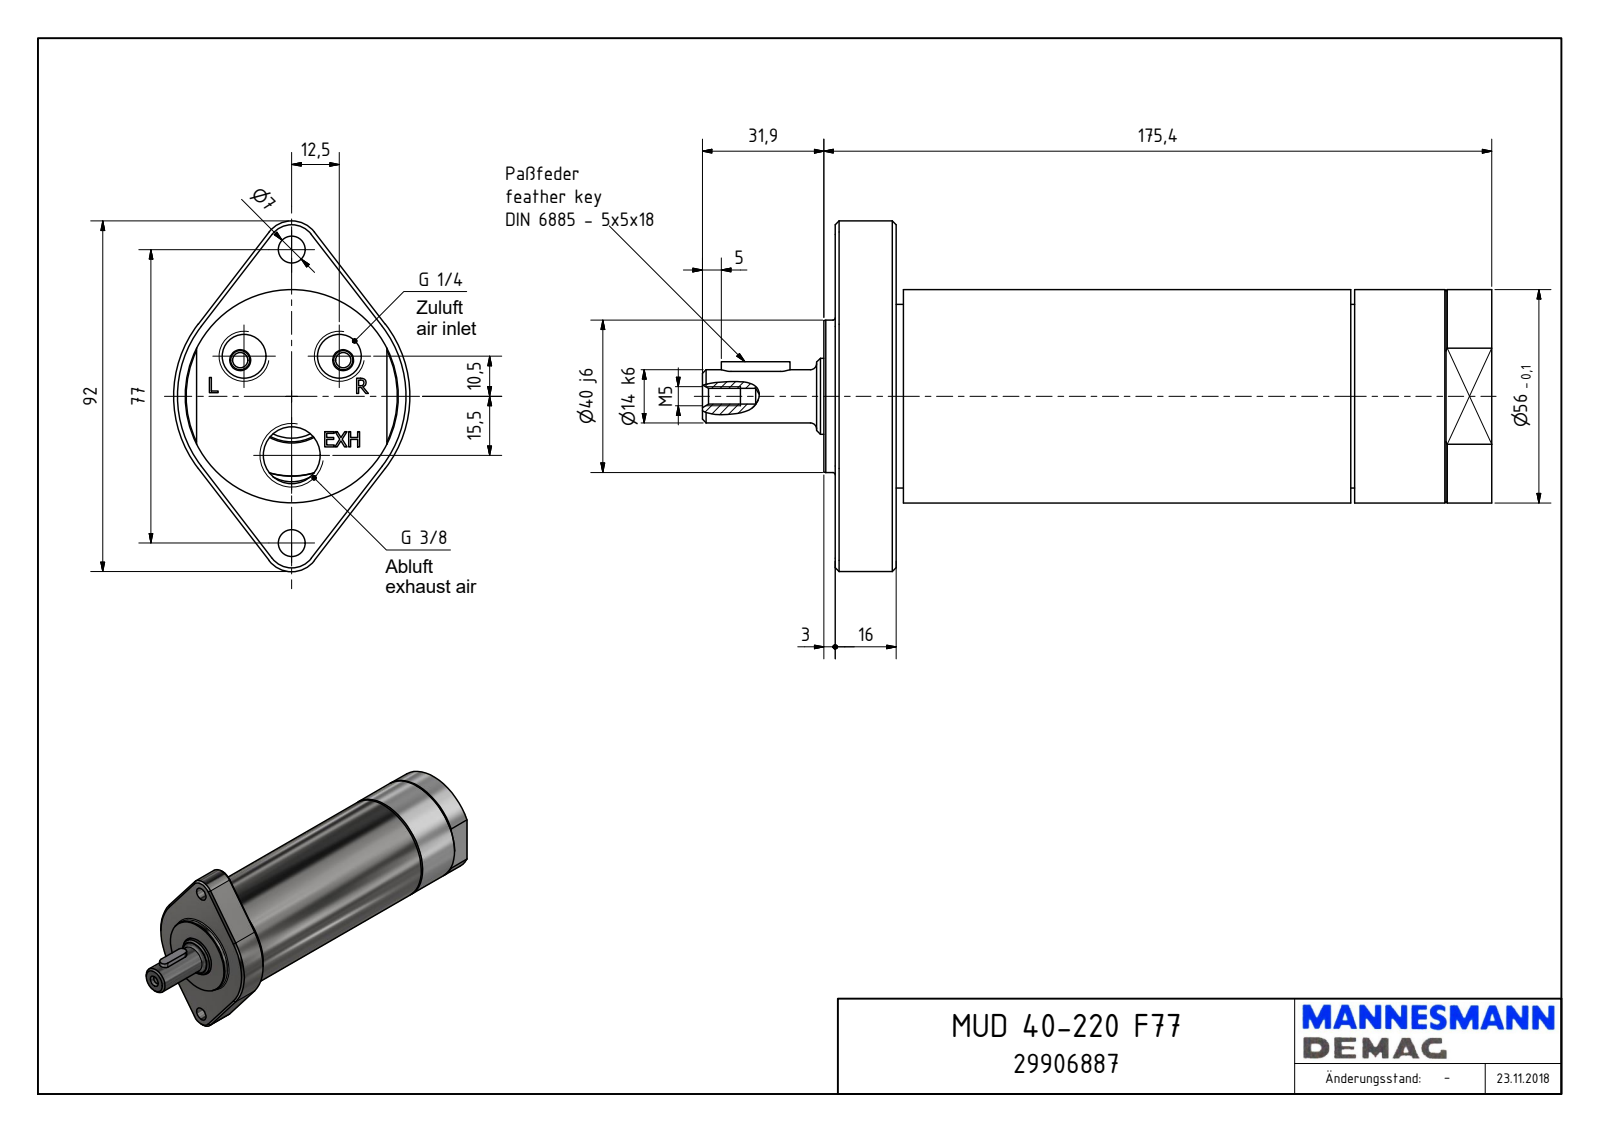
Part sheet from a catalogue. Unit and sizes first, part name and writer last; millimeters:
Units: millimetres
Overall size (bounding box): 207.3 × 92 × 62
Round holes (diameter × count): ⌀7 ×2, ⌀11.45 ×2, ⌀4.13 ×1, ⌀14.95 ×1, ⌀21 ×1, ⌀21.25 ×1, ⌀23.54 ×1, ⌀26 ×1, ⌀48.38 ×1
Round bosses / shafts (diameter × count): ⌀56 ×1, ⌀48.18 ×1, ⌀40 ×1, ⌀19.95 ×1, ⌀14 ×1
Partial cylindrical surfaces — rounded edges, fillets, slot ends (radius × count): R2.5 ×2, R6 ×2, R7.5 ×2, R19.57 ×1, R23 ×1, R31 ×1
Main face-to-face distances: 172.4, 16, 156.4, 3, 19, 175.4, 1.9, 20.9, 17.9, 154.5
Hole centre spacings: 16.32, 28.85, 30.66, 38.5, 50.57, 15.5, 23, 25
Volume: 444 470 mm³ · Surface area: 47 913 mm²
Bodies: 1 solid, 195 faces (105 planar, 36 cylindrical, 54 other)
Part name (STEP PRODUCT): MUD 40-220 F77_29906887
STEP written by: Autodesk Inventor 2018 (AUTOMOTIVE_DESIGN)
